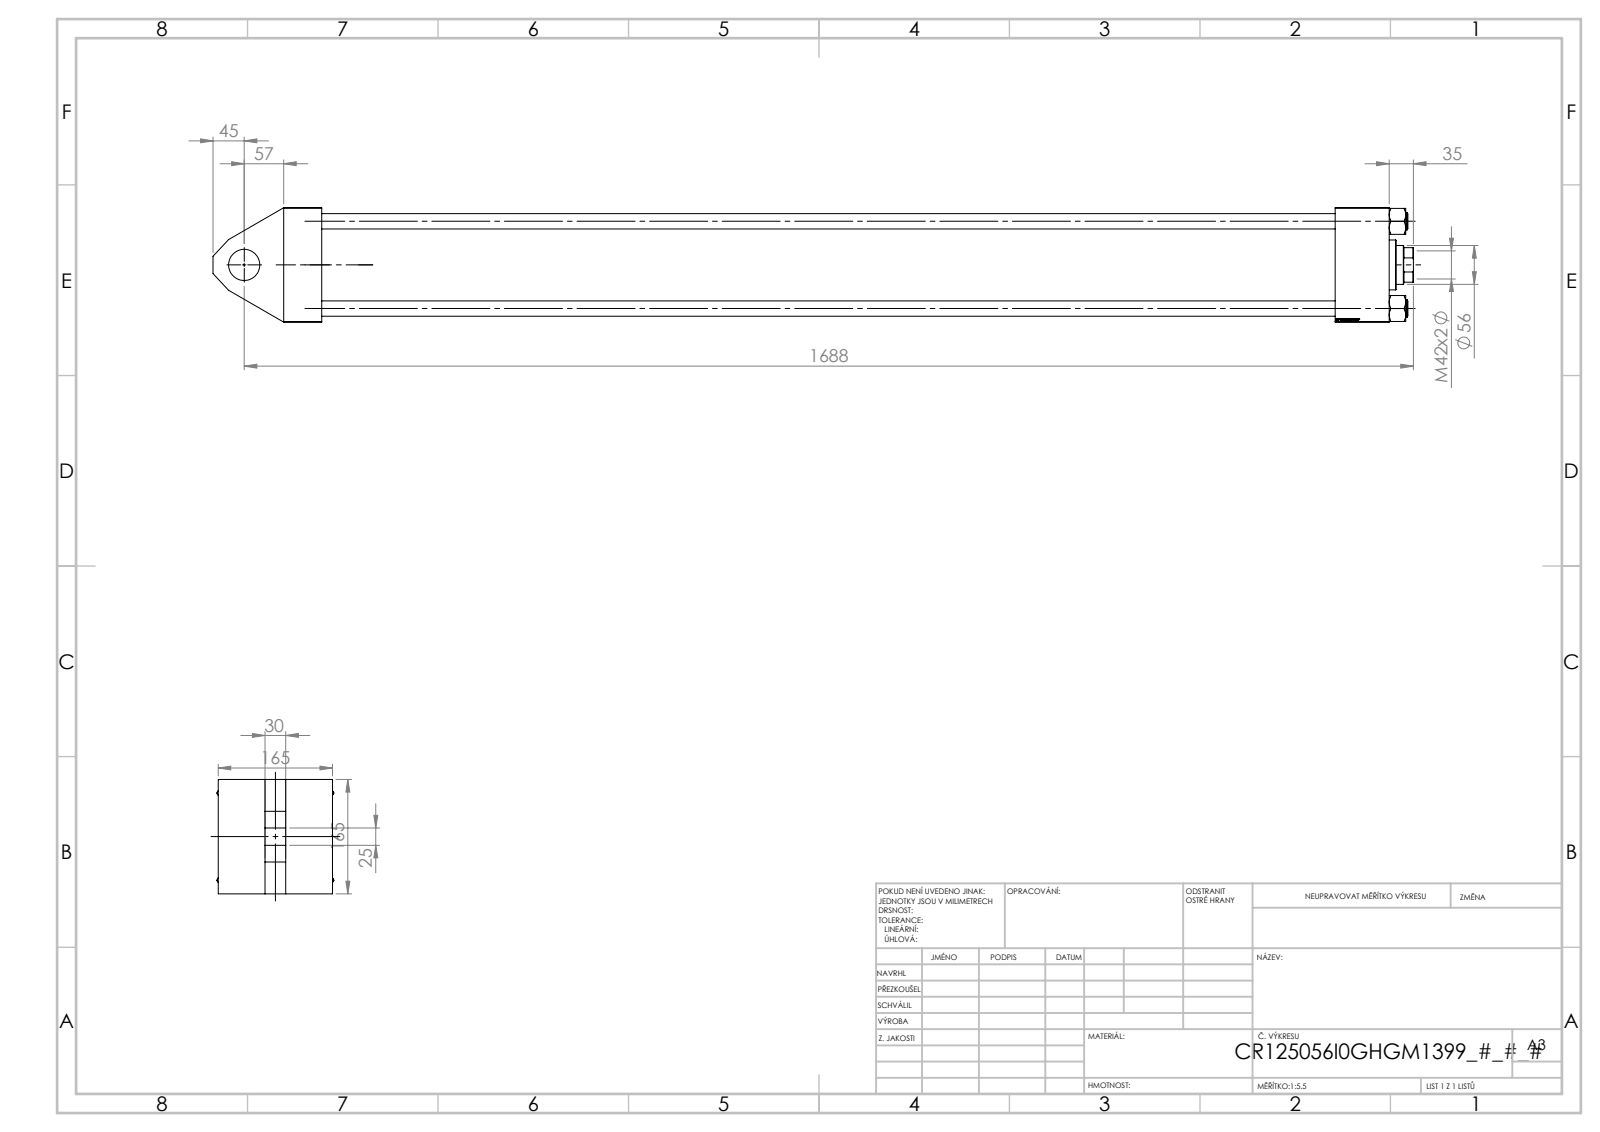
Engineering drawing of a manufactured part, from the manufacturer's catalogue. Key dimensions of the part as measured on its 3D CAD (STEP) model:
Part name (STEP PRODUCT): NUT_M5_I; V215CR_VCP_I; V215CR_I_Body; V215_VC_A (+1 more)
STEP written by: SolidWorks 2019 (CONFIG_CONTROL_DESIGN)
Units: millimetres
Bodies: 11 solids, 1127 faces (550 planar, 81 cylindrical, 496 other)
Overall size (bounding box): 1733 × 169.14 × 165
Volume: 11 970 000 mm³ · Surface area: 2 267 000 mm²
Round holes (diameter × count): ⌀22 ×4, ⌀45 ×3, ⌀7 ×2, ⌀32.24 ×2, ⌀40.5 ×1, ⌀56 ×1, ⌀59 ×1, ⌀96 ×1, ⌀125 ×1, ⌀125.5 ×1
Round bosses / shafts (diameter × count): ⌀25 ×4, ⌀131 ×1, ⌀72 ×1
Partial cylindrical surfaces — rounded edges, fillets, slot ends (radius × count): R27 ×1
Main face-to-face distances: 165, 1541, 55, 1596, 78, 67.5, 97.5, 1518, 1463, 1567.3
Hole centre spacings: 89.02, 125.9, 178.05, 84.5, 1517.5, 1602
